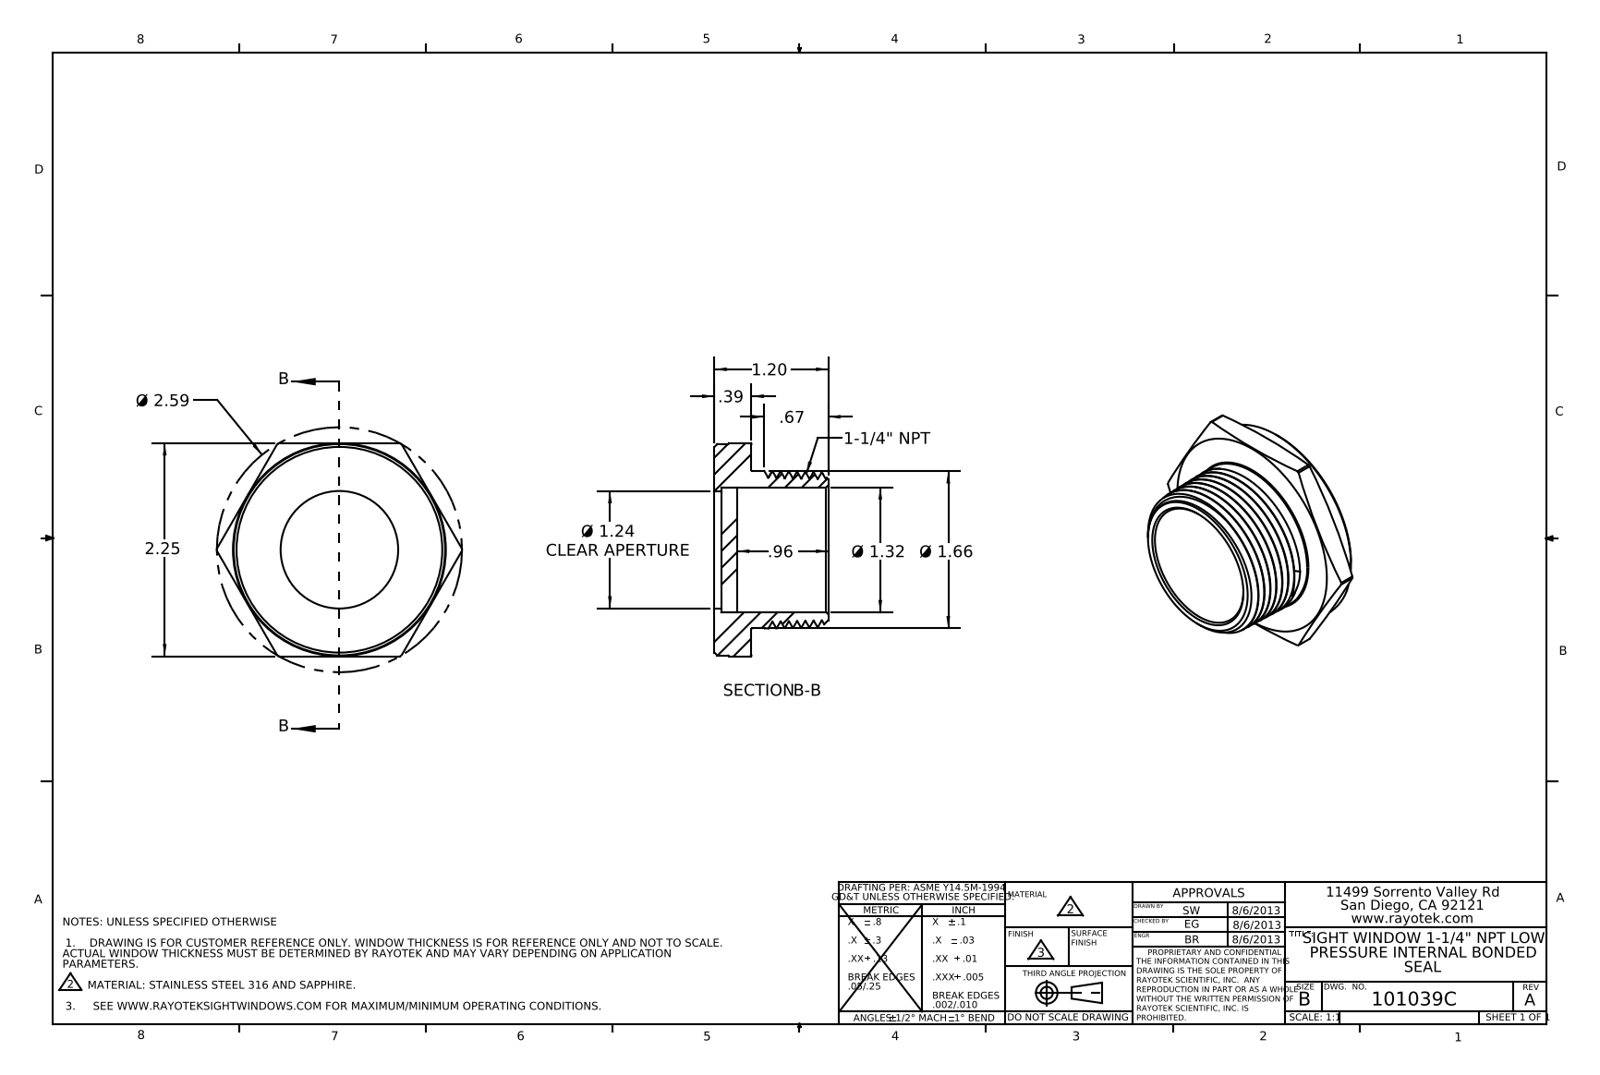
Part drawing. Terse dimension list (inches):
name: 403039
written by: SolidWorks 2012 (AUTOMOTIVE_DESIGN)
unit: in
bodies: 2 solids, 65 faces (15 planar, 17 cylindrical, 33 other)
size: 2.586 × 2.25 × 1.2
volume: 1.822 in³; area: 23.68 in²
holes: 1× ⌀1.24, 1× ⌀1.32
bosses: 1× ⌀2.23, 1× ⌀1.66
rounds: 1× R1.293
face distances: 0.39, 0.078, 0.312, 0.238, 0.16, 0.152, 2.25, 1.2, 1.122, 0.962
